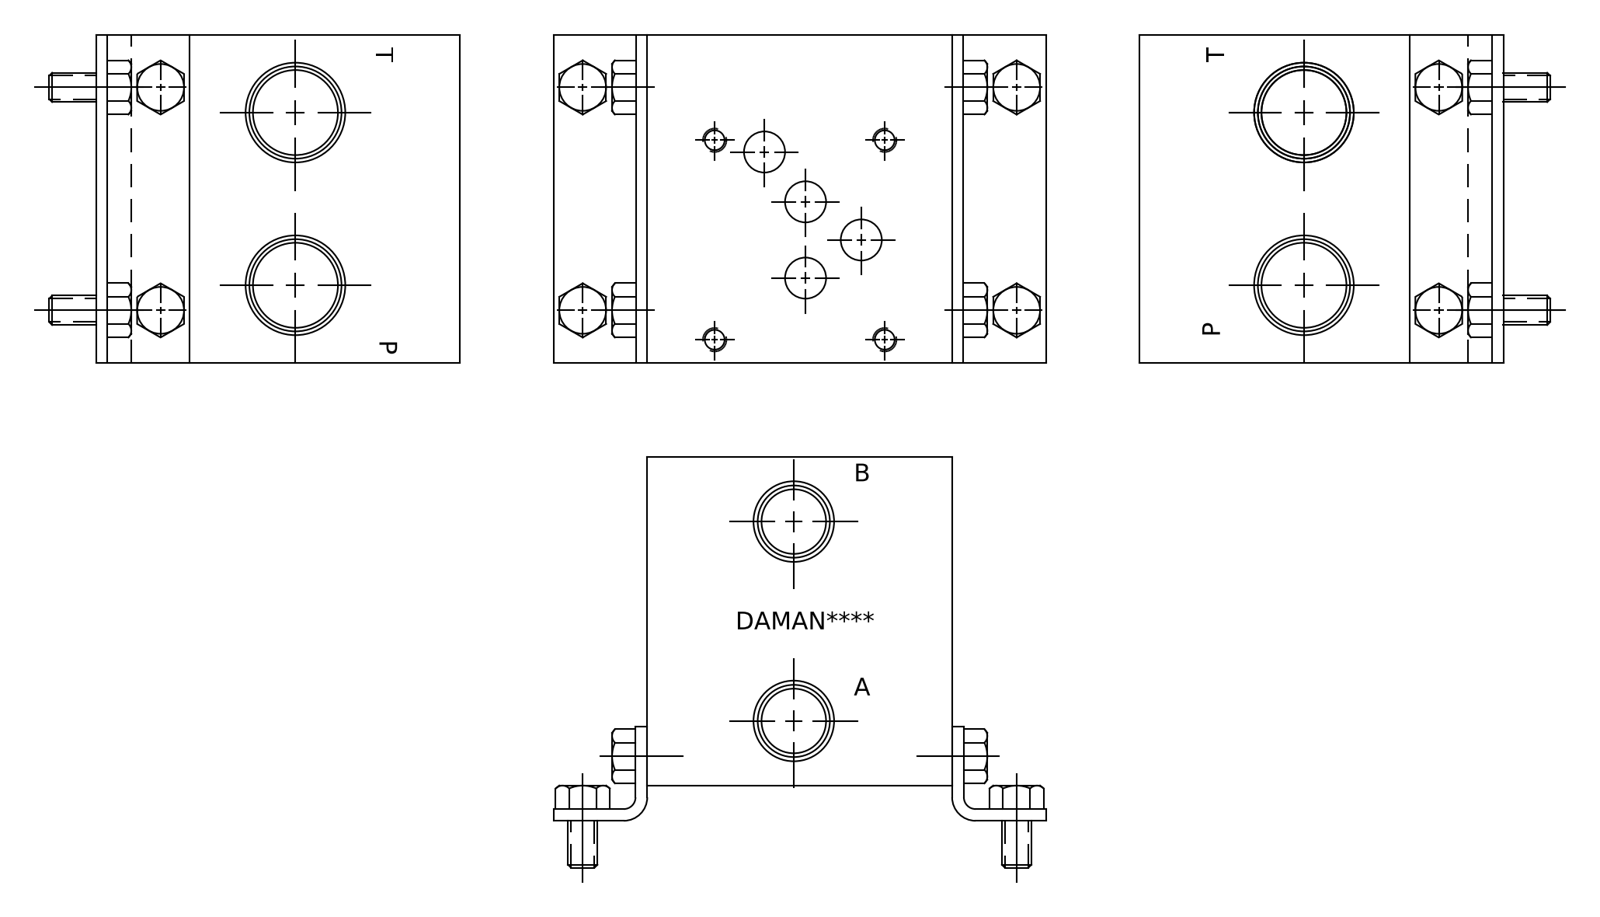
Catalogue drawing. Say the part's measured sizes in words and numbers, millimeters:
The part is named "Part_AD05P013P.C03350R6_3D". Its 3-D file was written by "Autodesk Inventor 2020 (AUTOMOTIVE_DESIGN)". It is 1 solid with 461 faces: 292 planar, 32 cylindrical and 137 other. Overall it measures 88.9 by 88.9 by 82.55 millimeters. Its volume is 592 036 cubic millimeters and its surface area 56 930 square millimeters. Round holes: 4 of diameter 5.11, 4 of diameter 6.35, 3 of diameter 11.13, 2 of diameter 6.53, 2 of diameter 7.92, 2 of diameter 17.48, 2 of diameter 21.59, 2 of diameter 23.01, 2 of diameter 26.92, 1 of diameter 11.11. The main face-to-face distances are 88.9, 82.55, 15.85, 66.7, 50.85, 15.37, 73.53, 15.33, 88.86, 11.18. The hole center spacings are 29.74, 37.16, 46.05, 64.82, 70.95, 13.88, 17.49, 18.28.
